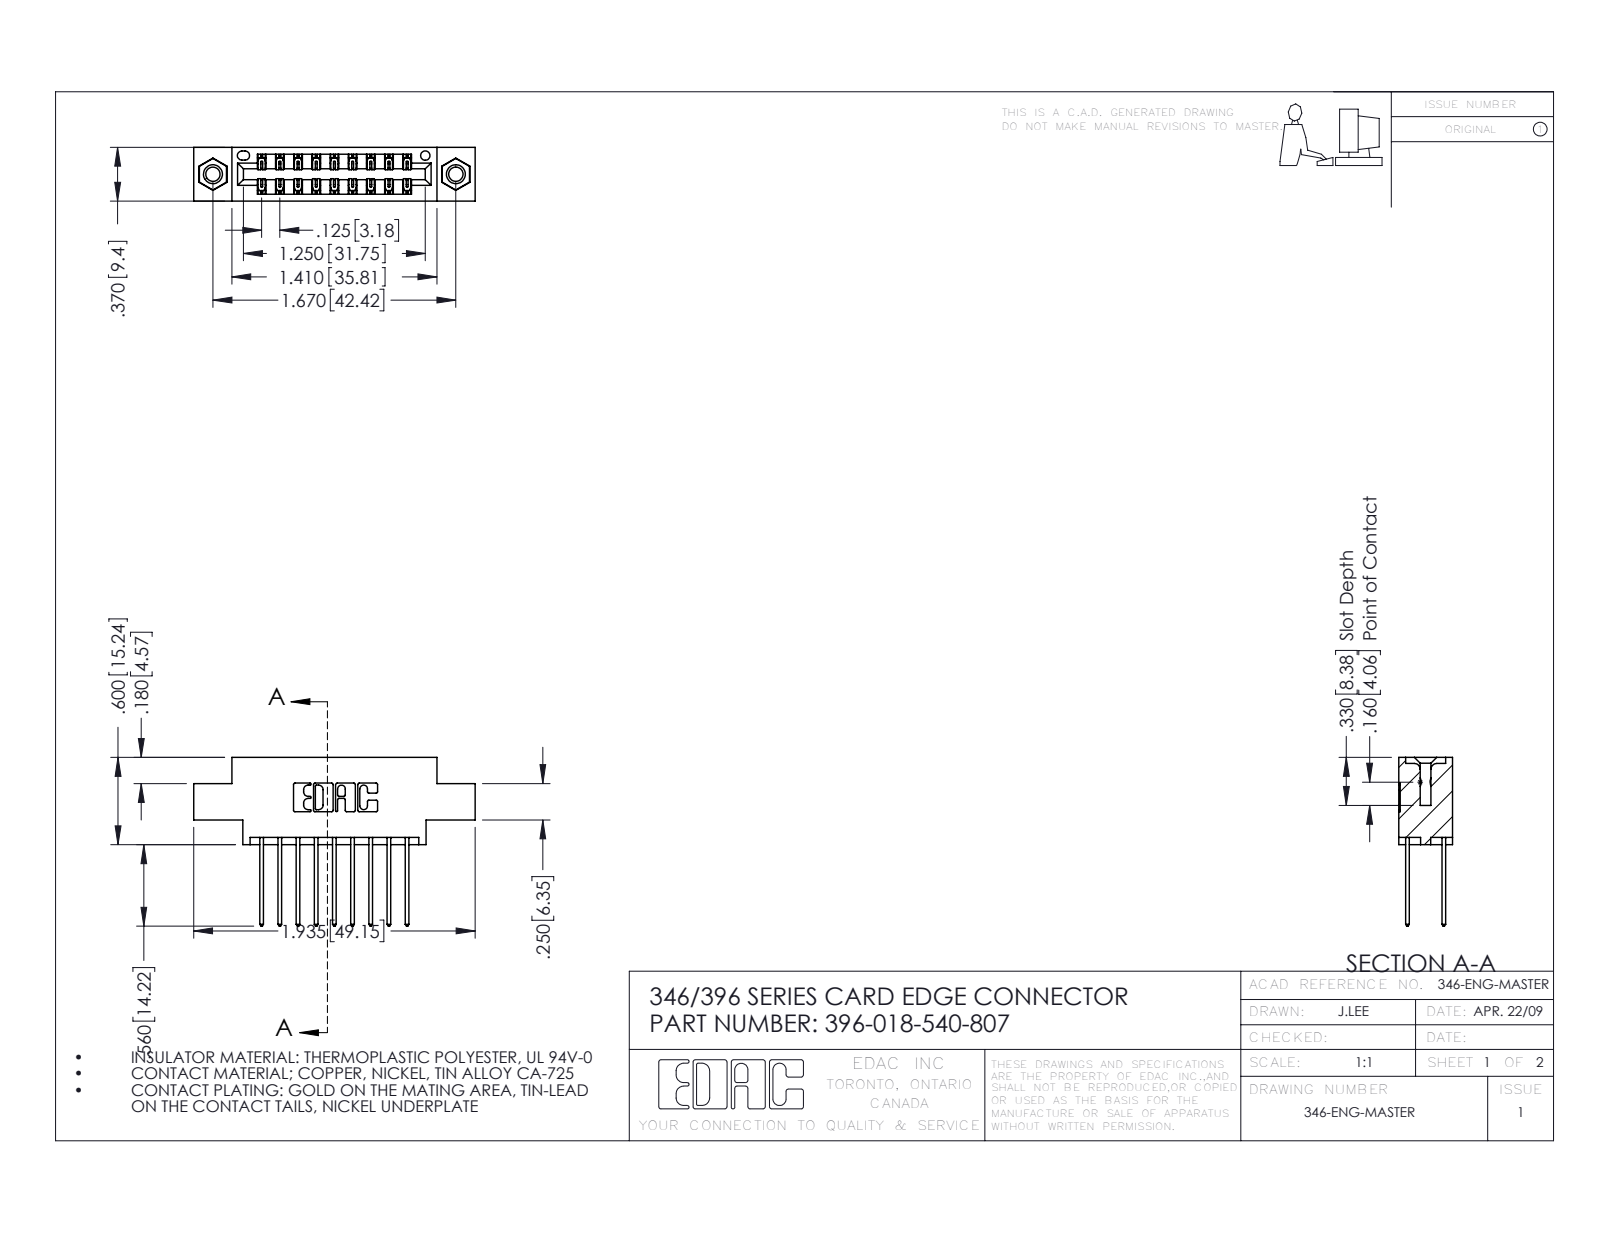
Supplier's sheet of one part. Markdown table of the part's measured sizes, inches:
| quantity | value |
| --- | --- |
| part name | 396-018-540-807; 345-250-001_345-250-005-103; 345-292-001_345-293-140; 346 Part_0.170 Offset - 0.156 Dia-TI |
| STEP written by | SolidWorks 2016 (CONFIG_CONTROL_DESIGN) |
| units | inches |
| bodies | 21 solids, 1122 faces (742 planar, 364 cylindrical, 16 other) |
| overall size | 1.935 × 1.16 × 0.37 |
| volume | 0.271 in³ |
| surface area | 9.479 in² |
| round holes (diameter × count) | 0.098 × 2, 0.125 × 2, 0.156 × 2, 0.064 × 1 |
| round bosses / shafts (diameter × count) | 0.155 × 2 |
| partial cylindrical surfaces (radius × count) | 0.006 × 27, 0.01 × 22, 0.01 × 18, 0.007 × 6, 0.031 × 6, 0.026 × 3, 0.014 × 2, 0.022 × 2 |
| main face-to-face distances | 0.25, 0.048, 0.322, 0.37, 0.072, 0.298, 0.025, 0.275, 0.222, 0.148 |
| hole center spacings | 0.246, 1.465, 1.67 |
